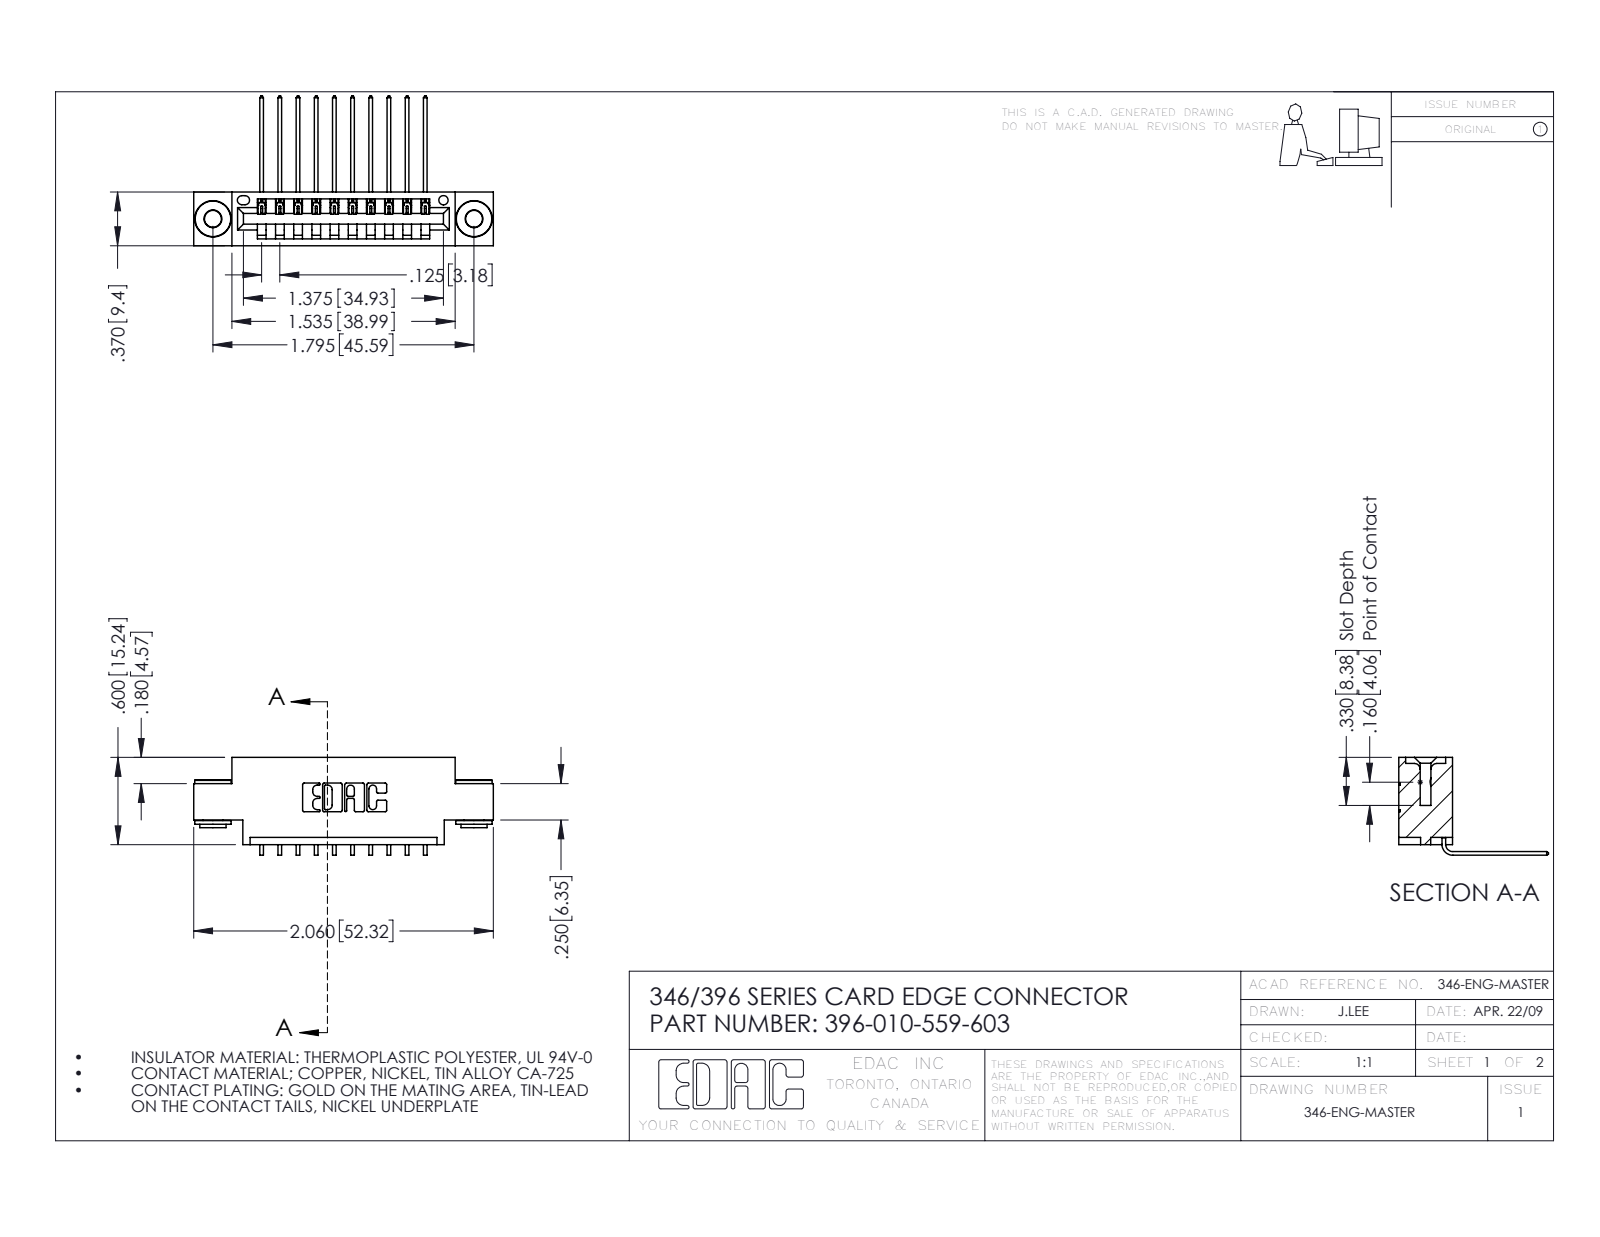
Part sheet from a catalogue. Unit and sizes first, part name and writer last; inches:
Units: inches
Overall size (bounding box): 2.06 × 1.03 × 0.673
Round holes (diameter × count): ⌀0.116 ×2, ⌀0.156 ×2, ⌀0.064 ×1
Round bosses / shafts (diameter × count): ⌀0.25 ×2, ⌀0.18 ×2, ⌀0.136 ×2
Partial cylindrical surfaces — rounded edges, fillets, slot ends (radius × count): R0.01 ×22, R0.006 ×20, R0.007 ×6, R0.031 ×6, R0.026 ×3, R0.031 ×2, R0.04 ×2, R0.014 ×1
Main face-to-face distances: 0.25, 0.37, 0.048, 0.322, 0.025, 0.072, 0.148, 0.222, 0.1, 0.174
Hole centre spacings: 0.246, 1.59, 1.795
Volume: 0.286 in³ · Surface area: 9.44 in²
Bodies: 13 solids, 764 faces (510 planar, 246 cylindrical, 8 other)
Part name (STEP PRODUCT): 345-250-002_345-250-002-102; 346 Part_0.170 Offset - 0.156 Dia-TH; 396-010-559-603; 345-292-001_558 559 Tail - 1
STEP written by: SolidWorks 2016 (CONFIG_CONTROL_DESIGN)
